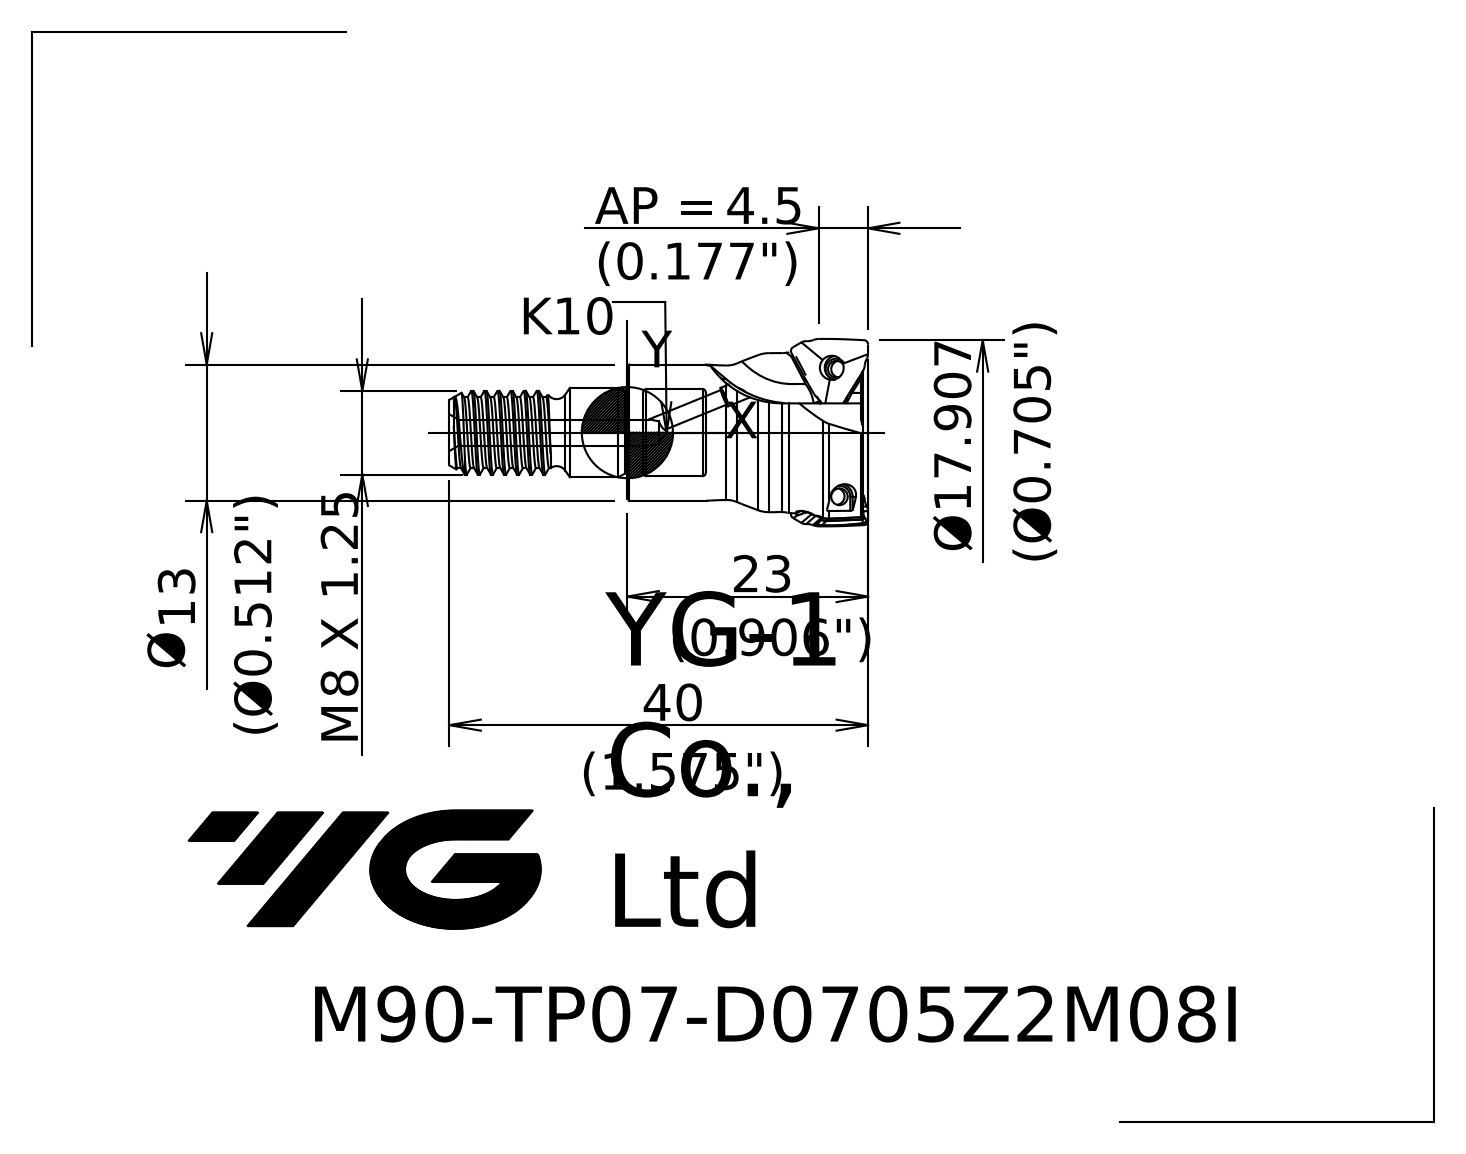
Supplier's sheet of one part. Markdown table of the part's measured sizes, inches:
| quantity | value |
| --- | --- |
| part name | 1022418019A30qwf |
| STEP written by | SIEMENS PLM Software NX 10.0 (AP203_CONFIGURATION_CONTROLLED_3D_DESIGN_OF_MECHANICAL_PARTS_AND_ASSEMBLIES_MIM_LF) |
| units | inches |
| bodies | 1 solid, 67 faces (10 planar, 11 cylindrical, 46 other) |
| overall size | 1.574 × 0.707 × 0.707 |
| volume | 0.26 in³ |
| surface area | 4.622 in² |
| round holes (diameter × count) | 0.059 × 1, 0.098 × 1 |
| round bosses / shafts (diameter × count) | 0.598 × 1, 0.512 × 1, 0.335 × 1, 0.315 × 1, 0.266 × 1 |
| partial cylindrical surfaces (radius × count) | 0.012 × 4 |
| main face-to-face distances | 0.394, 0.88, 0.885, 1.555, 1.549, 0.669, 0.59, 0.584, 0.295, 0.965 |
